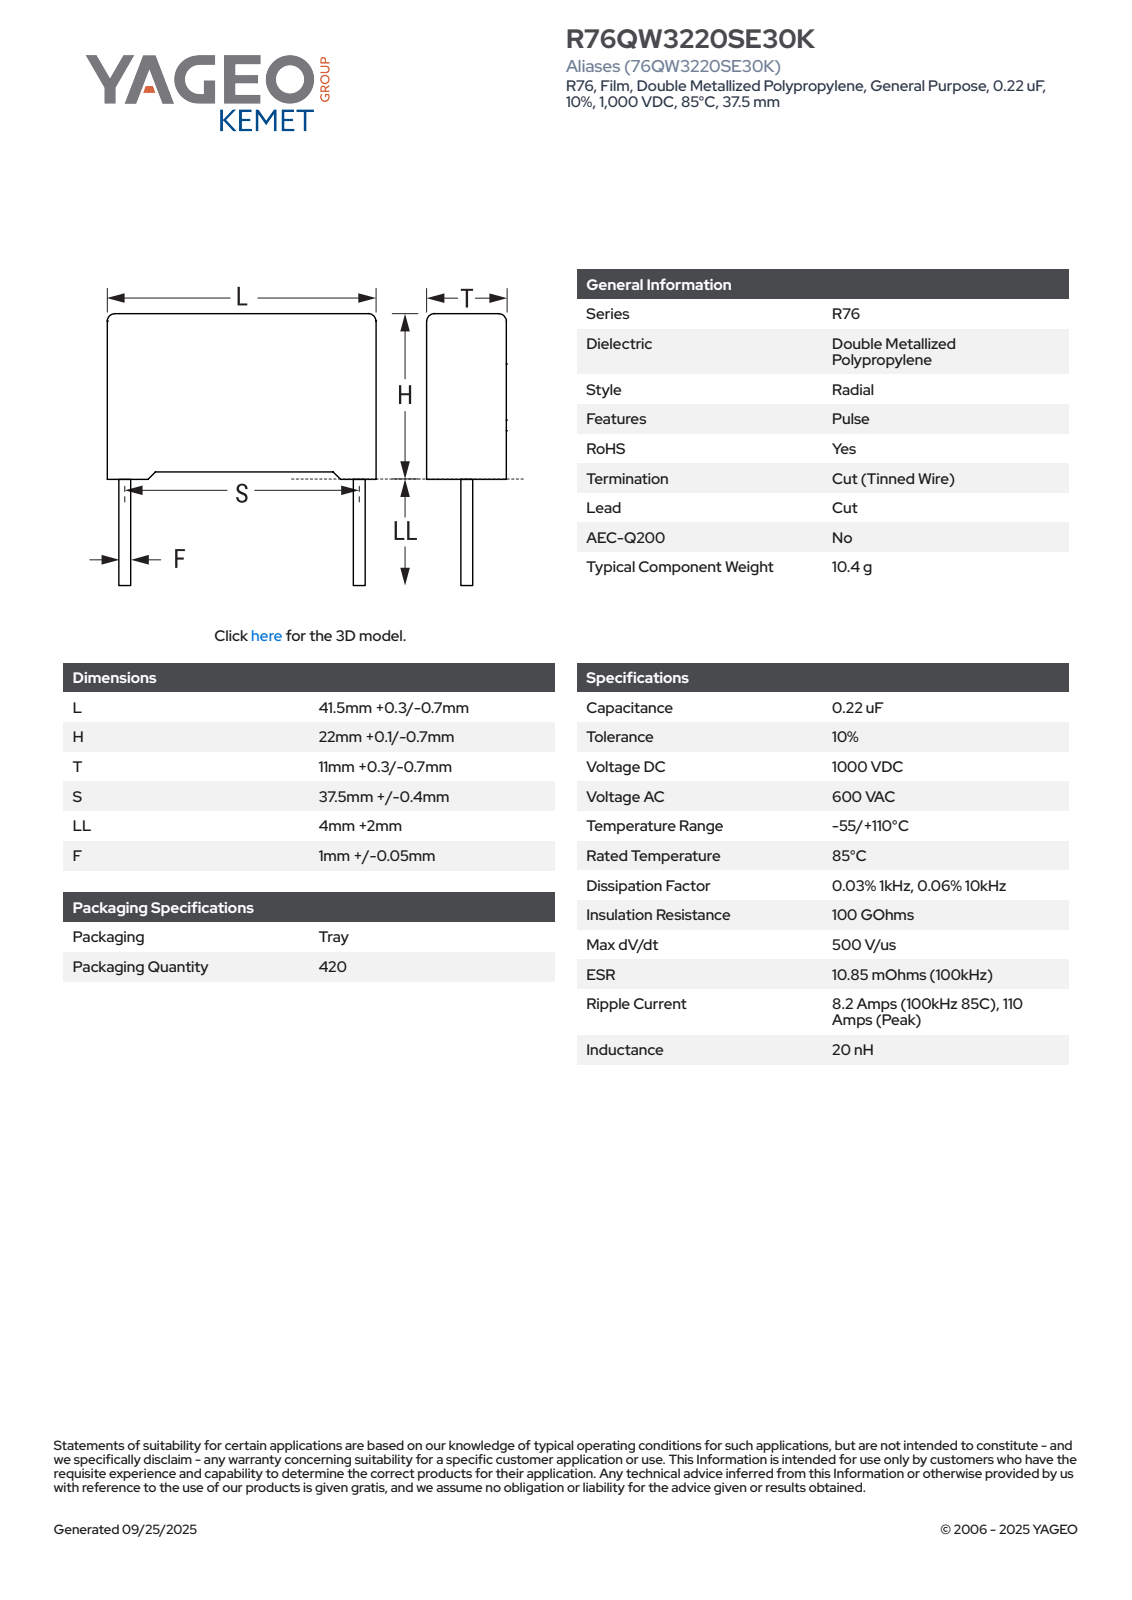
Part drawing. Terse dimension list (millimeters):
name: CFR_RB2_41.5X22X11_L41.8H22.1T11.3S37.5LL6F1.05
written by: SolidWorks 2021 (AUTOMOTIVE_DESIGN)
unit: mm
bodies: 4 solids, 85 faces (77 planar, 8 cylindrical, 0 other)
size: 41.8 × 28.1 × 11.3
volume: 10 122 mm³; area: 3 416 mm²
bosses: 2× ⌀1.05
rounds: 4× R0.5
face distances: 11.3, 21.34, 41.8, 21.35, 0.75, 0.76, 22.1, 11.31, 1.39, 40.41
